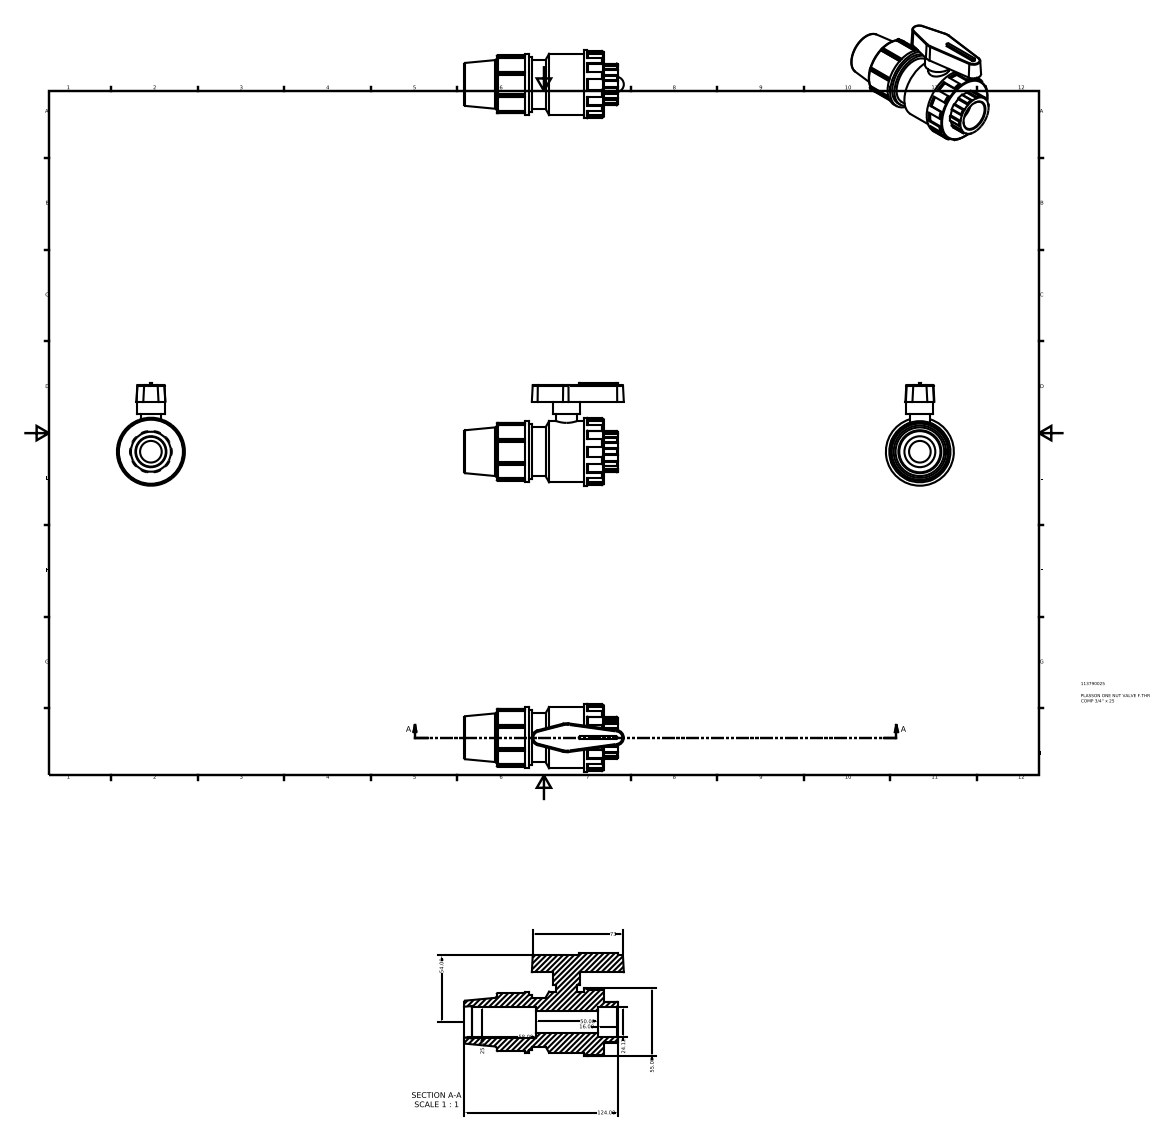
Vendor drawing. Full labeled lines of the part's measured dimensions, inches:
Part name (STEP PRODUCT): 113790025
STEP written by: Autodesk Inventor 2015 (AUTOMOTIVE_DESIGN)
Units: inches
Bodies: 1 solid, 248 faces (99 planar, 74 cylindrical, 75 other)
Overall size (bounding box): 5.078 × 3.272 × 2.165
Volume: 10.4 in³ · Surface area: 57.04 in²
Round holes (diameter × count): ⌀0.689 ×1, ⌀0.95 ×1, ⌀0.984 ×1
Round bosses / shafts (diameter × count): ⌀2.165 ×1, ⌀2.079 ×1, ⌀1.949 ×1, ⌀1.851 ×1, ⌀1.754 ×1, ⌀1.559 ×1, ⌀0.866 ×1, ⌀0.65 ×1
Partial cylindrical surfaces — rounded edges, fillets, slot ends (radius × count): R0.028 ×20, R0.03 ×16, R0.019 ×4, R0.043 ×2, R0.636 ×1, R0.665 ×1
Main face-to-face distances: 0.531, 0.63, 0.441, 1.028, 3.811, 4.441, 2.055, 1.756, 2.386, 2.288
